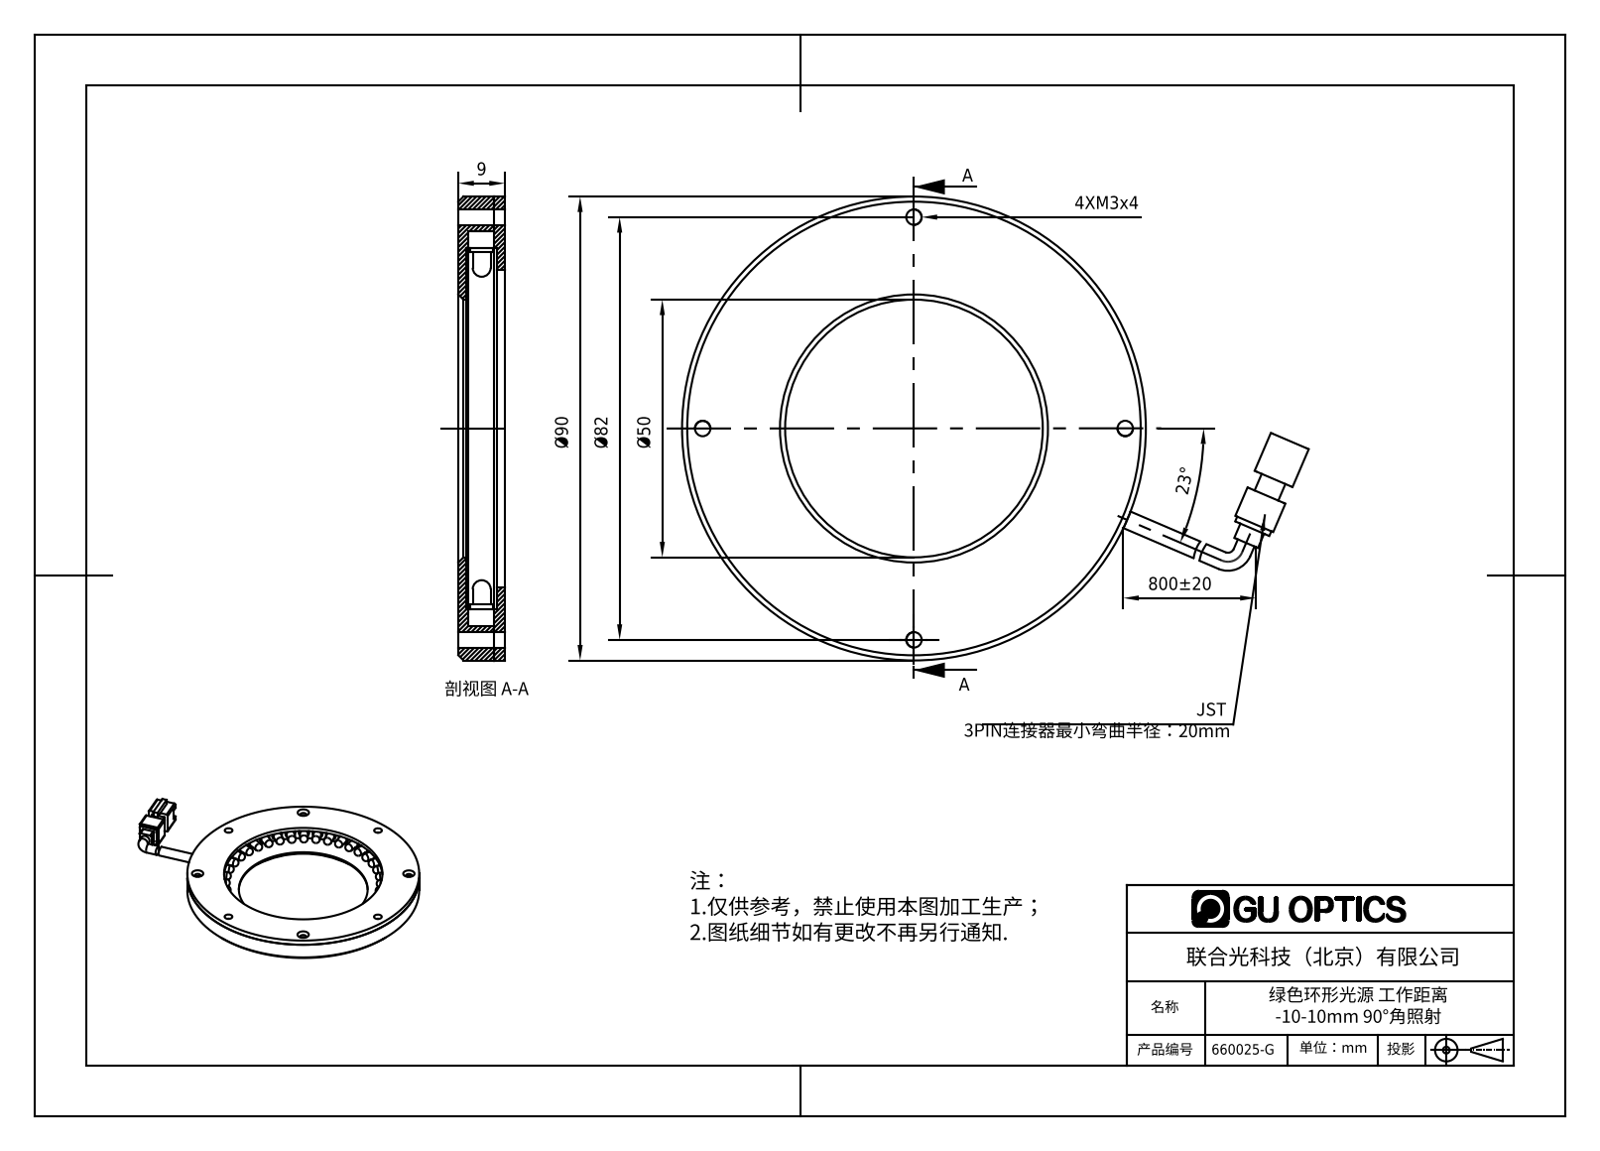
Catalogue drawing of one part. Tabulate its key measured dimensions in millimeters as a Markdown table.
| quantity | value |
| --- | --- |
| part name | 660025-G |
| STEP written by | SolidWorks 2016 (AUTOMOTIVE_DESIGN) |
| units | millimeters |
| bodies | 45 solids, 884 faces (553 planar, 267 cylindrical, 64 other) |
| overall size | 121.62 × 90 × 10 |
| volume | 25 302 mm³ |
| surface area | 28 044 mm² |
| round holes (diameter × count) | 3 × 8, 1.6 × 4, 2 × 4, 2.4 × 4, 3.5 × 2, 50 × 1, 61.48 × 1, 69 × 1, 70 × 1, 76.68 × 1 |
| round bosses / shafts (diameter × count) | 3.8 × 40, 3 × 40, 3.5 × 2, 90 × 1, 69.4 × 1 |
| partial cylindrical surfaces (radius × count) | 0.5 × 8, 1 × 4, 1.8 × 2, 5 × 1, 33.5 × 1, 37.1 × 1 |
| main face-to-face distances | 7, 2, 9, 1.5, 5.5, 7.5, 0.5, 6, 5, 1 |
| hole center spacings | 75.76, 82, 31.38, 41, 57.98, 31.35, 31.41, 57.96 |
